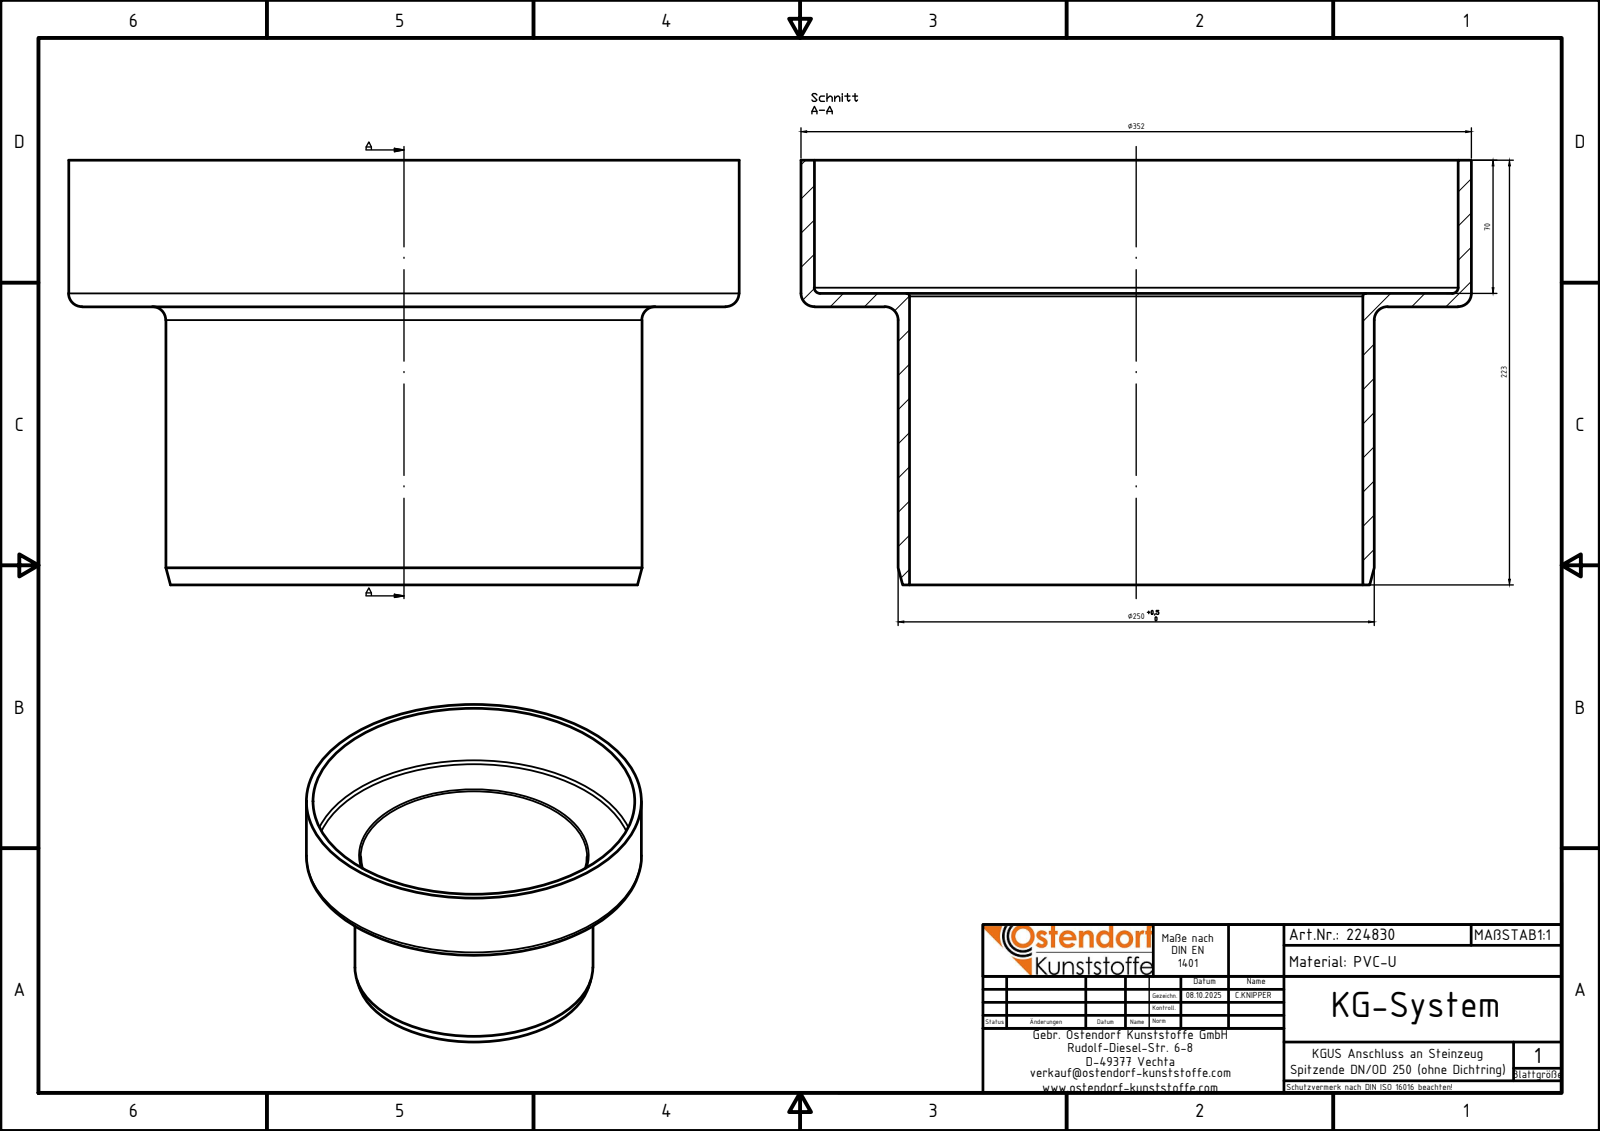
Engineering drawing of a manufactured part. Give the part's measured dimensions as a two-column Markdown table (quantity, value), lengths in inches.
| quantity | value |
| --- | --- |
| part name | 224830z |
| STEP written by | Autodesk Inventor 2024 (AUTOMOTIVE_DESIGN) |
| units | inches |
| bodies | 1 solid, 13 faces (4 planar, 4 cylindrical, 5 other) |
| overall size | 13.858 × 13.858 × 8.78 |
| volume | 95.32 in³ |
| surface area | 751.7 in² |
| round holes (diameter × count) | 9.37 × 1, 13.307 × 1 |
| round bosses / shafts (diameter × count) | 13.858 × 1, 9.843 × 1 |
| main face-to-face distances | 0.276, 3.031, 2.756, 5.748, 6.024, 8.78 |
